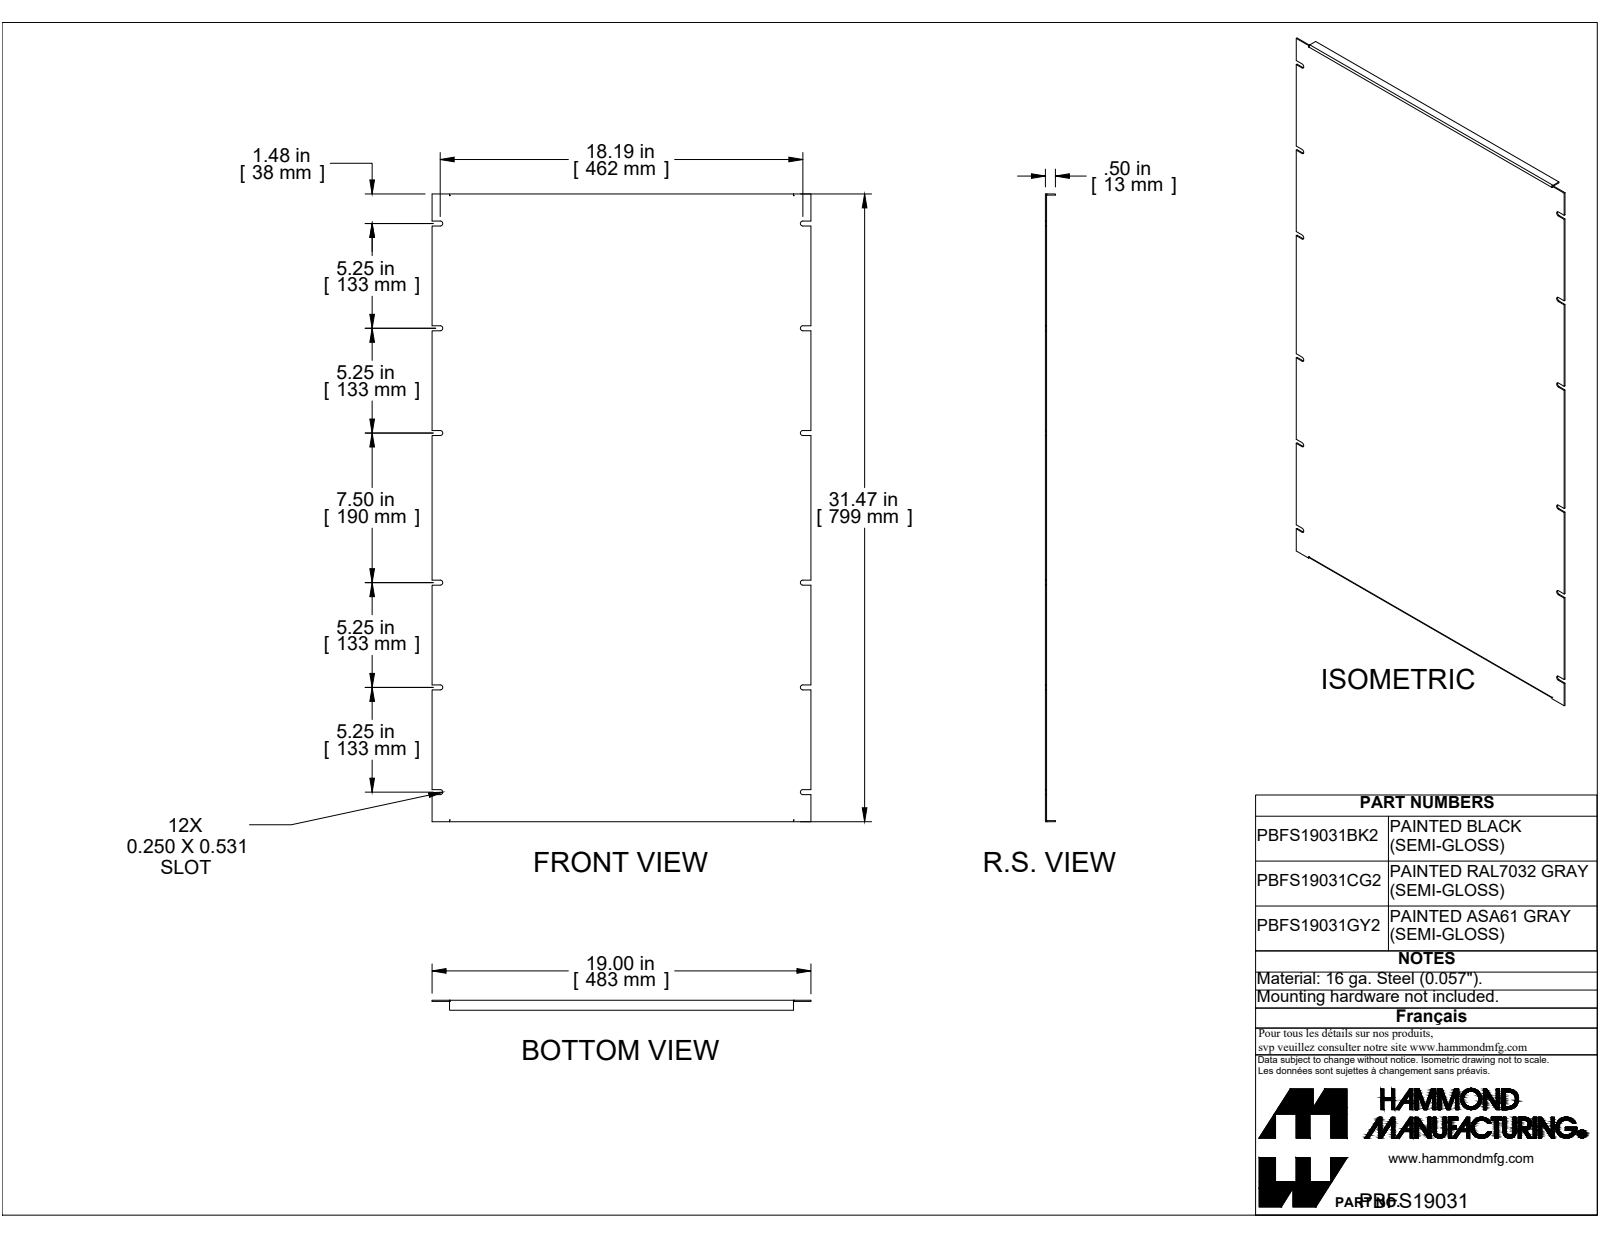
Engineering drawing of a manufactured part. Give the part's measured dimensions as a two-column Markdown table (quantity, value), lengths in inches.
| quantity | value |
| --- | --- |
| part name | PBFS19031 |
| STEP written by | SolidWorks 2019 (CONFIG_CONTROL_DESIGN) |
| units | inches |
| bodies | 1 solid, 78 faces (62 planar, 16 cylindrical, 0 other) |
| overall size | 31.468 × 19 × 0.5 |
| volume | 34.82 in³ |
| surface area | 1 228 in² |
| partial cylindrical surfaces (radius × count) | 0.125 × 12, 0.029 × 2, 0.086 × 2 |
| main face-to-face distances | 0.057, 0.057, 31.411, 31.468, 31.354, 0.5, 0.443, 19, 5.25, 0.25 |
